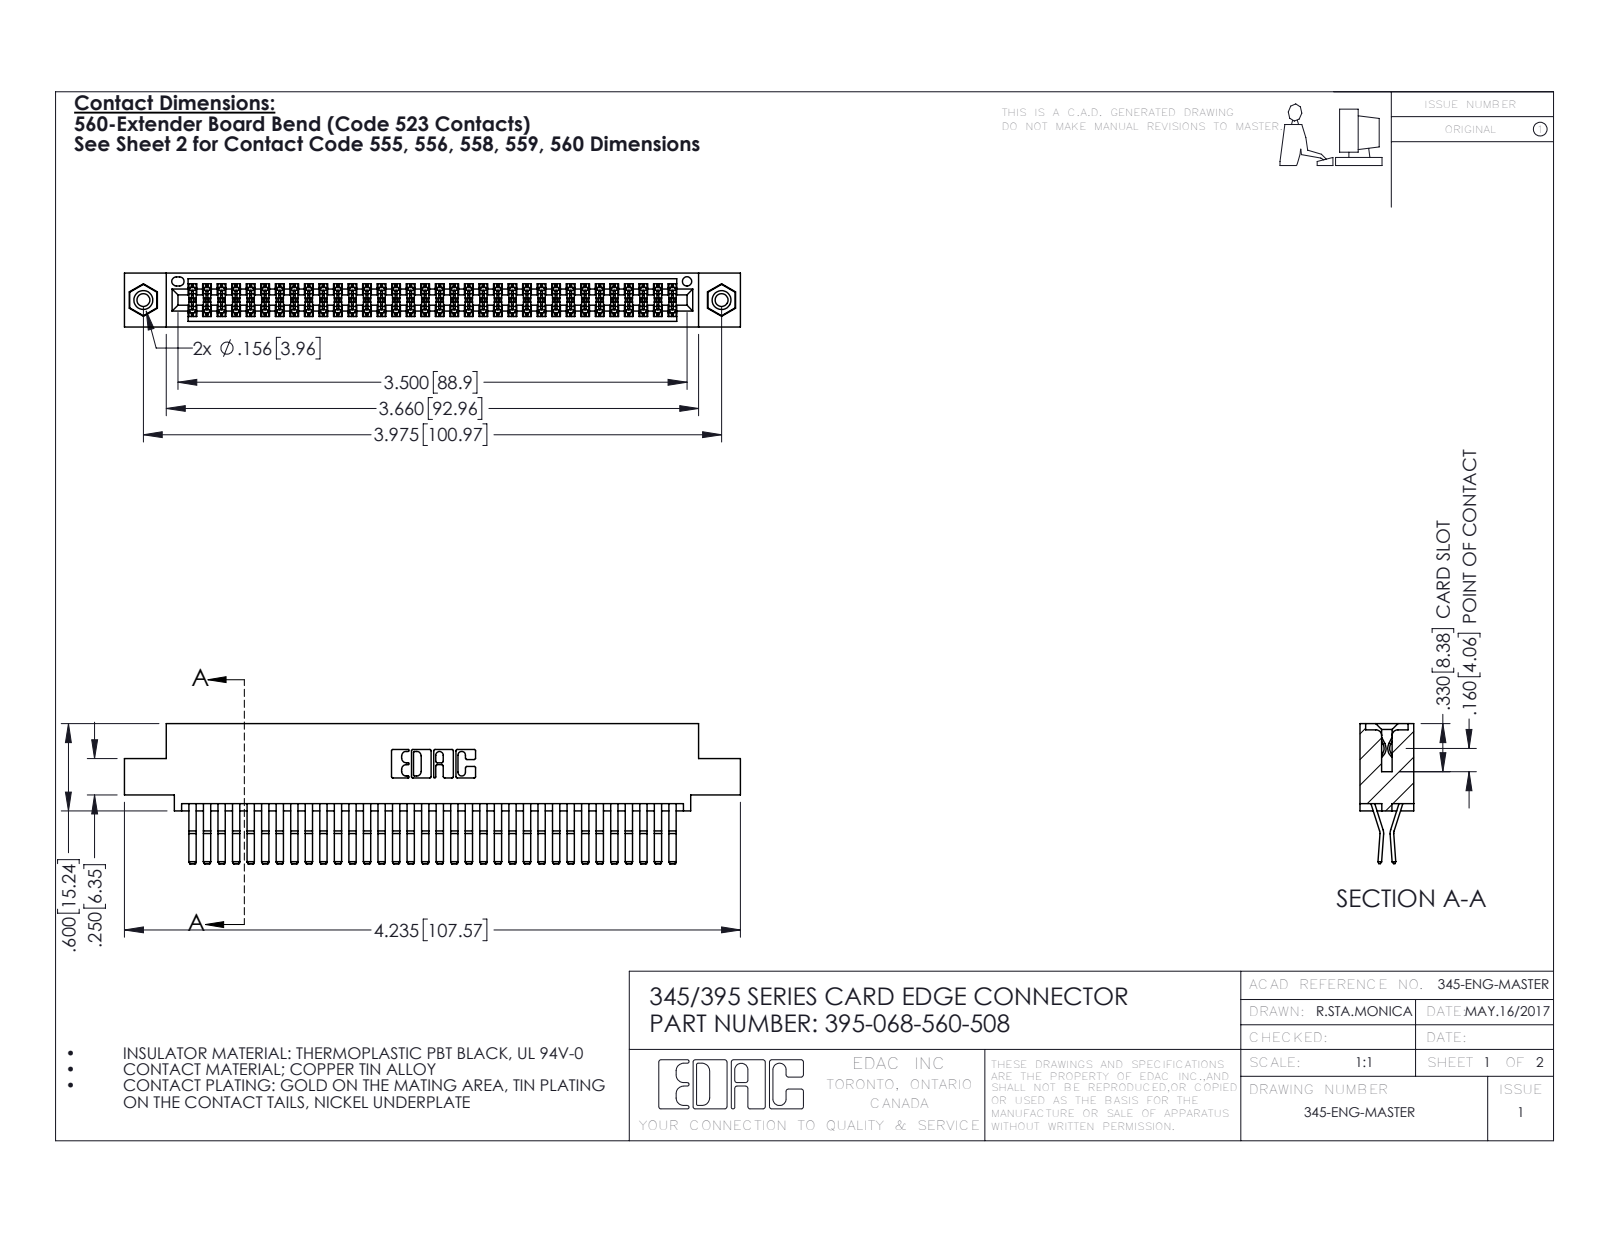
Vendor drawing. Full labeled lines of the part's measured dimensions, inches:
Part name (STEP PRODUCT): 345-250-001_345-250-003-102; 395-068-560-508; 345 Part_0.110 Offset - 0.156 Dia-TI; 345-292-001_560 Tail
STEP written by: SolidWorks 2016 (CONFIG_CONTROL_DESIGN)
Units: inches
Bodies: 71 solids, 3726 faces (2360 planar, 1350 cylindrical, 16 other)
Overall size (bounding box): 4.235 × 0.962 × 0.37
Volume: 0.655 in³ · Surface area: 26.31 in²
Round holes (diameter × count): ⌀0.089 ×2, ⌀0.125 ×2, ⌀0.156 ×2, ⌀0.064 ×1
Round bosses / shafts (diameter × count): ⌀0.155 ×2
Partial cylindrical surfaces — rounded edges, fillets, slot ends (radius × count): R0.006 ×102, R0.01 ×22, R0.007 ×6, R0.031 ×6, R0.026 ×3, R0.01 ×2, R0.014 ×2, R0.019 ×2
Main face-to-face distances: 0.025, 0.072, 0.298, 0.37, 0.2, 0.098, 0.272, 0.225, 0.175, 0.149
Hole centre spacings: 0.27, 3.74, 3.975
